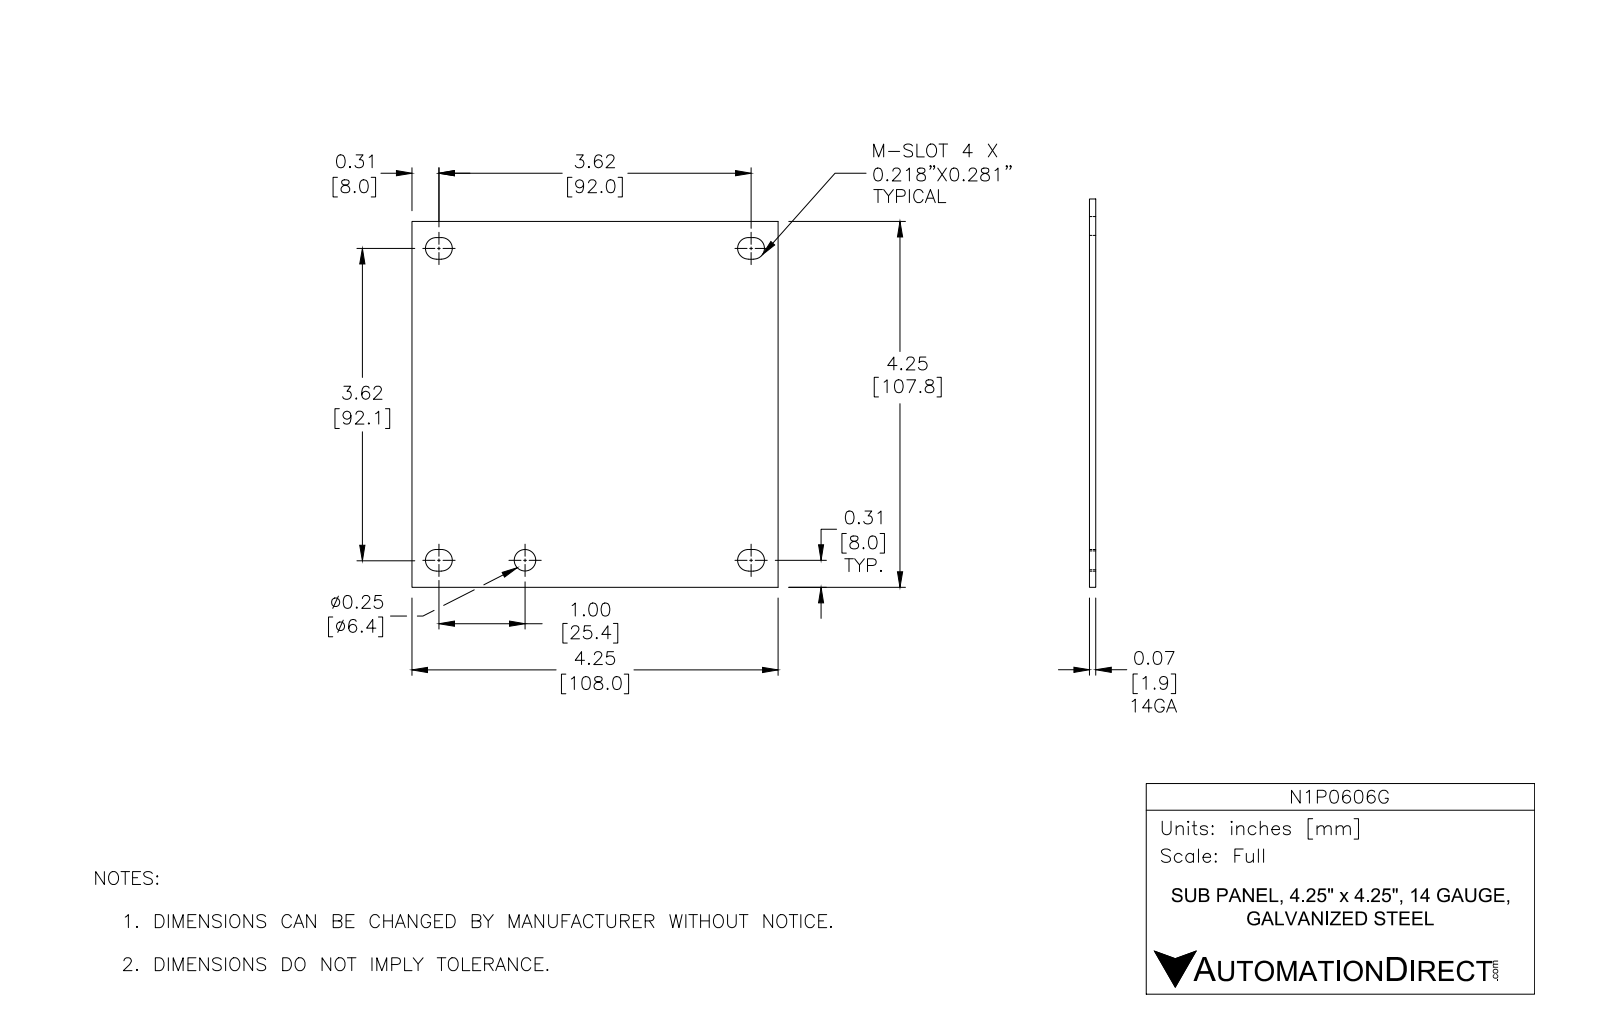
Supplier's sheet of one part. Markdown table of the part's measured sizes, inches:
| quantity | value |
| --- | --- |
| part name | N1P0606 |
| STEP written by | Autodesk Inventor 2012 (AUTOMOTIVE_DESIGN) |
| units | inches |
| bodies | 1 solid, 23 faces (14 planar, 9 cylindrical, 0 other) |
| overall size | 4.25 × 4.25 × 0.074 |
| volume | 1.314 in³ |
| surface area | 37.1 in² |
| round holes (diameter × count) | 0.25 × 1 |
| partial cylindrical surfaces (radius × count) | 0.125 × 8 |
| main face-to-face distances | 0.074, 4.25, 0.188, 0.438, 3.812, 4.062, 0.25, 3.624, 3.874, 3.374 |
